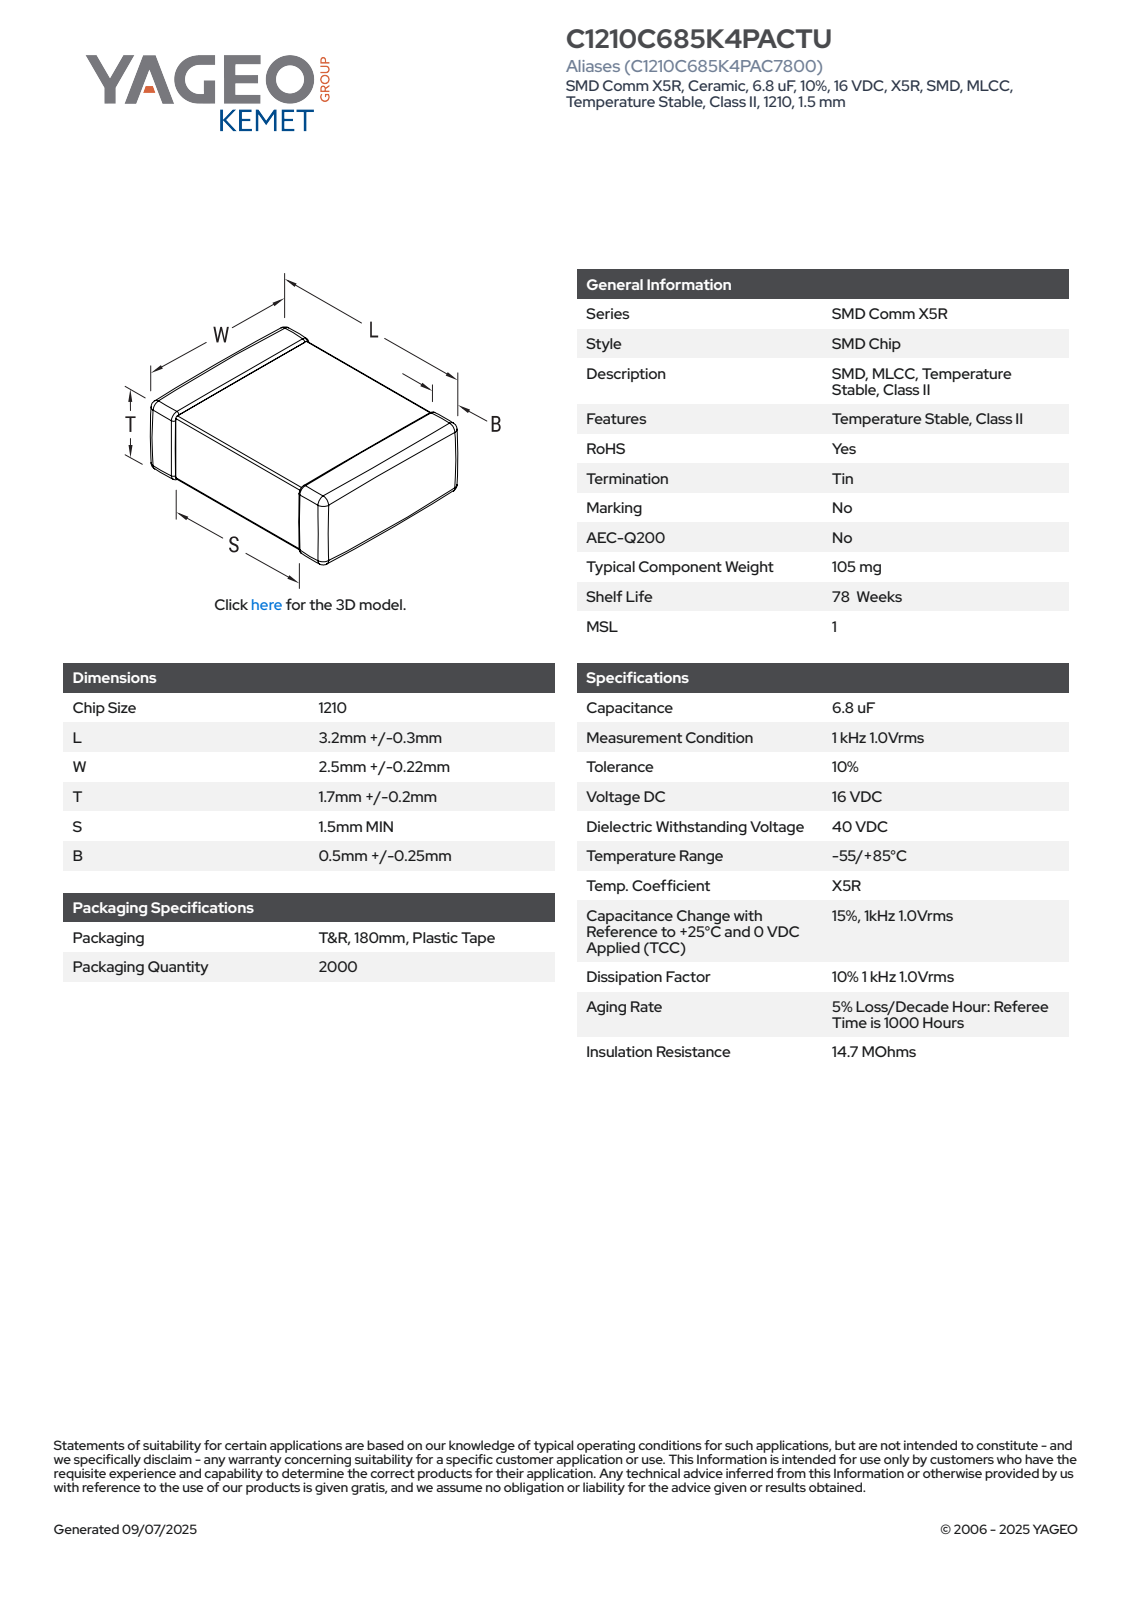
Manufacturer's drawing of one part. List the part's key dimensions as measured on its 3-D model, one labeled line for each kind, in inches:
Part name (STEP PRODUCT): CCS_CCSTDNOS_1210_L3.4W2.7T2.05B0.75
STEP written by: SolidWorks 2014 (AUTOMOTIVE_DESIGN)
Units: inches
Bodies: 4 solids, 125 faces (71 planar, 38 cylindrical, 16 other)
Overall size (bounding box): 0.134 × 0.106 × 0.081
Volume: 0.001 in³ · Surface area: 0.067 in²
Main face-to-face distances: 0.078, 0.134, 0.104, 0.076, 0.102, 0.081, 0.106, 0.079, 0.076, 0.052
